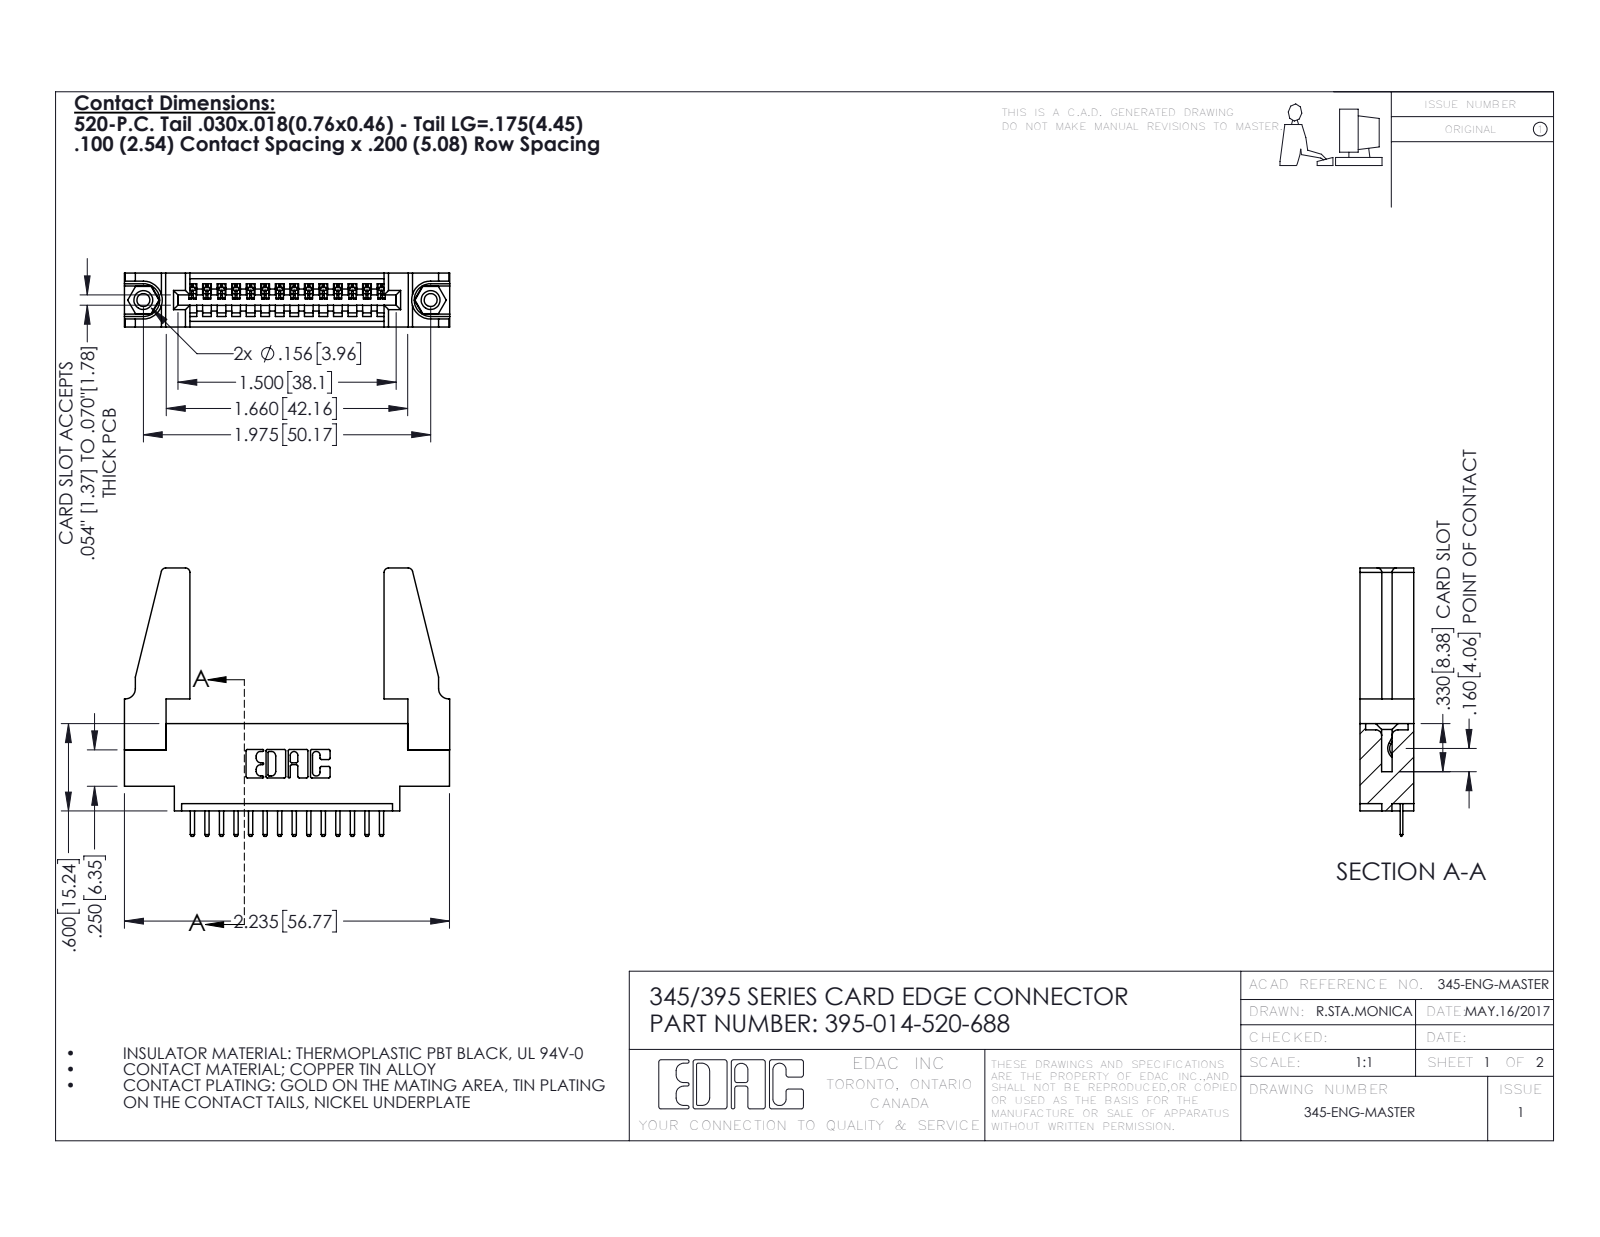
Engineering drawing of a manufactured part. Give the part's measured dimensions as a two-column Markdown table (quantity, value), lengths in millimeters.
| quantity | value |
| --- | --- |
| part name | 345-250-001_345-250-001-102; 395-014-520-688; 345-220-078_345-220-088; 345-292-001_345-293-120 (+1 more) |
| STEP written by | SolidWorks 2016 (CONFIG_CONTROL_DESIGN) |
| units | millimeters |
| bodies | 19 solids, 1122 faces (744 planar, 362 cylindrical, 16 other) |
| overall size | 56.8 × 46.9 × 9.4 |
| volume | 8 260 mm³ |
| surface area | 9 400 mm² |
| round holes (diameter × count) | 2.3 × 2, 3.2 × 2, 4 × 2, 1.6 × 1 |
| round bosses / shafts (diameter × count) | 3.9 × 2 |
| partial cylindrical surfaces (radius × count) | 0.3 × 30, 0.2 × 28, 0.3 × 22, 0.8 × 8, 0.2 × 6, 0.8 × 6, 0.7 × 3, 0.8 × 2 |
| main face-to-face distances | 9.4, 1.8, 7.6, 5.1, 2.5, 6.9, 0.6, 5.7, 3.8, 3.8 |
| hole center spacings | 6.9, 44.2, 50.2 |
